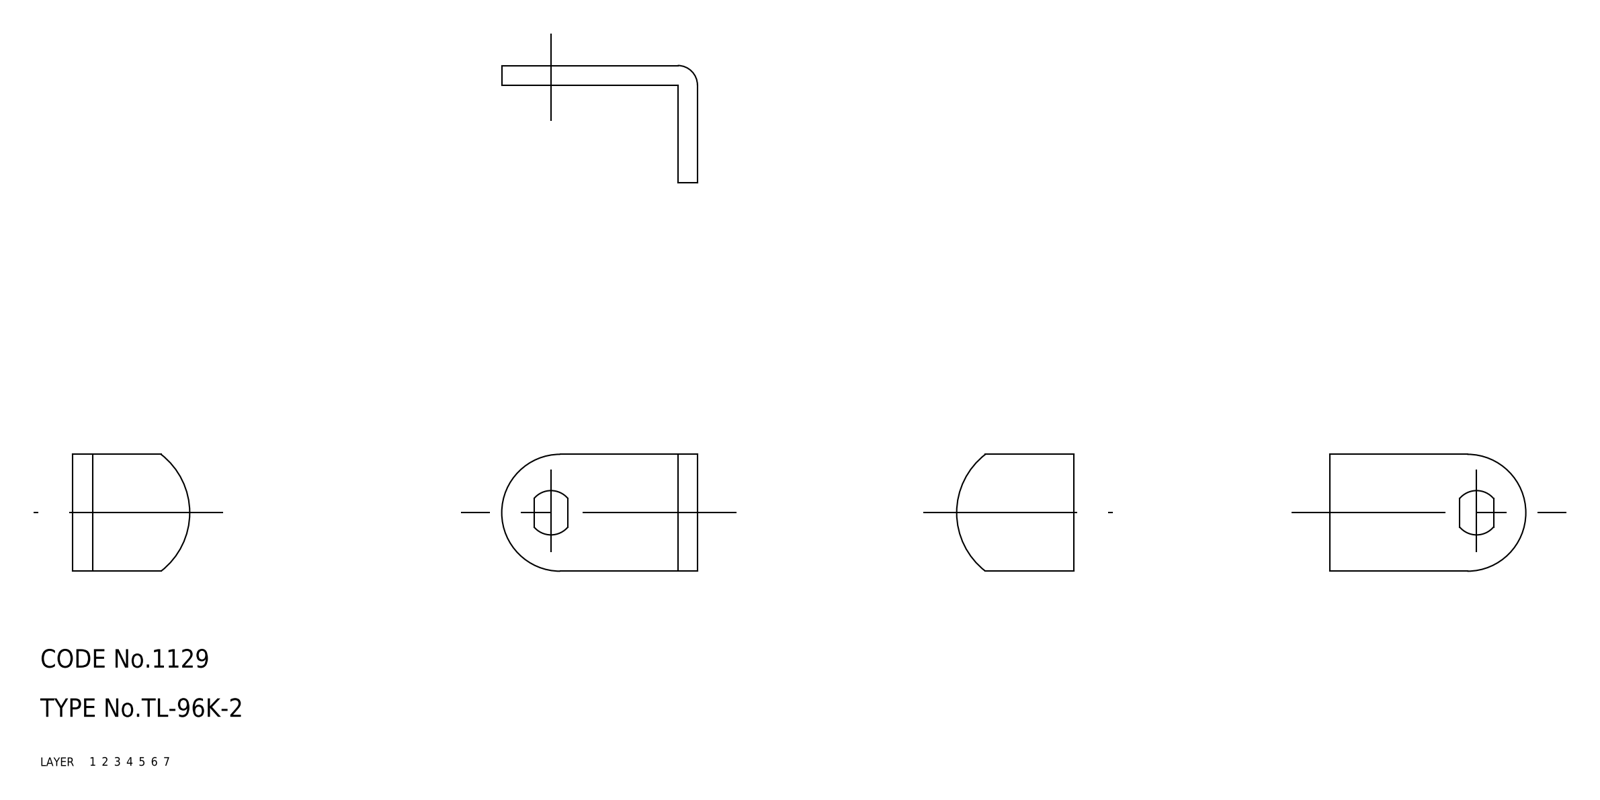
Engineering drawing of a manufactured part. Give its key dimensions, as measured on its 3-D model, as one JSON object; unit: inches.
{"part_name": "cam", "step_written_by": "CADfix (AUTOMOTIVE_DESIGN)", "units": "inches", "bodies": {"solids": 1, "faces": 13, "planar": 0, "cylindrical": 0, "other": 13}, "overall_size": [1.252, 0.748, 0.748], "volume_in3": 0.154, "surface_area_in2": 3.14}
